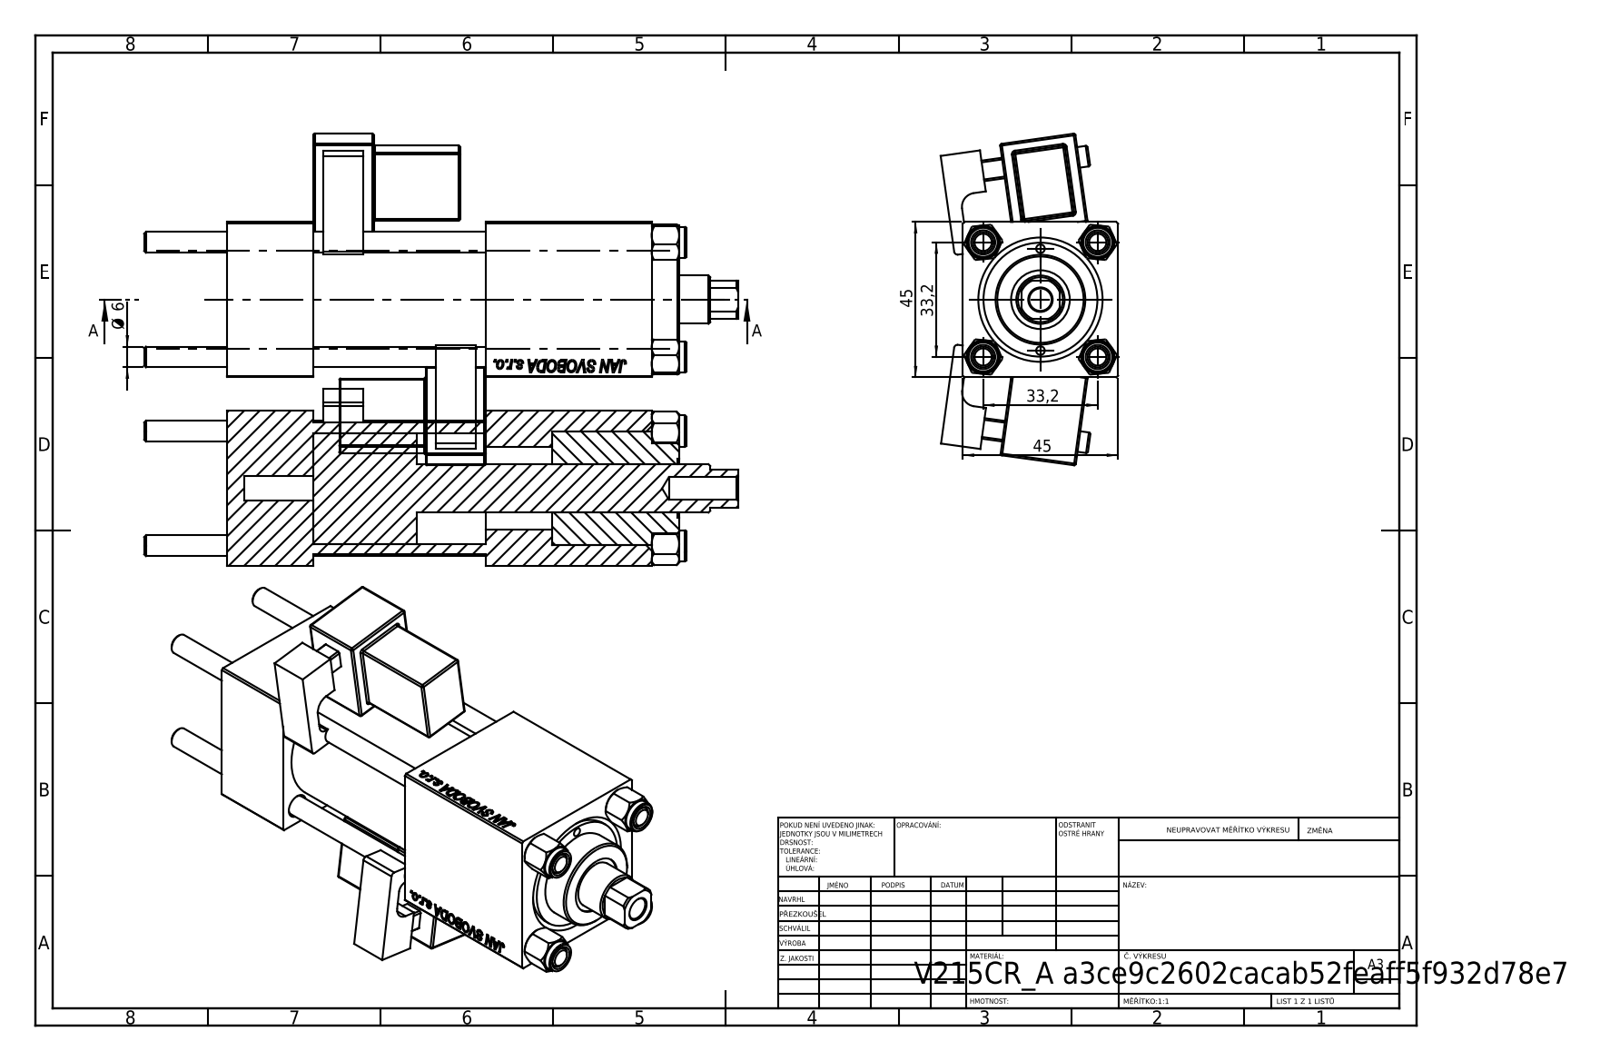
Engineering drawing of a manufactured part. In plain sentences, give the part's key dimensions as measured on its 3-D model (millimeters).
The part is named "V215_VC_A; NUT_M5; V215CR_MSU; CR025_012_A_0_G_A_G_M_020_+#_##_TYCINKA (+2 more)". Its 3-D file was written by "SolidWorks 2019 (CONFIG_CONTROL_DESIGN)". It is 13 solids with 1297 faces: 583 planar, 142 cylindrical and 572 other. Overall it measures 172 by 96.03 by 51.41 millimeters. Its volume is 238 920 cubic millimeters and its surface area 84 903 square millimeters. Round holes: 4 of diameter 6, 2 of diameter 2.5, 2 of diameter 7, 2 of diameter 13.16, 2 of diameter 20, 1 of diameter 6.5, 1 of diameter 14, 1 of diameter 17, 1 of diameter 24, 1 of diameter 32, 1 of diameter 33. Round bosses or shafts: 4 of diameter 9, 2 of diameter 6, 1 of diameter 38, 1 of diameter 26. Partial cylindrical surfaces (rounded edges, fillets, slot ends): 48 of radius 0.5, 2 of radius 1, 2 of radius 2.5, 2 of radius 4, 1 of radius 6.5. The main face-to-face distances are 45, 25, 3, 50, 75, 98, 123, 15, 48, 32.5. The hole center spacings are 16.7, 23.48, 33.2, 35.47, 14.75, 46.95, 29.5, 75.5.
